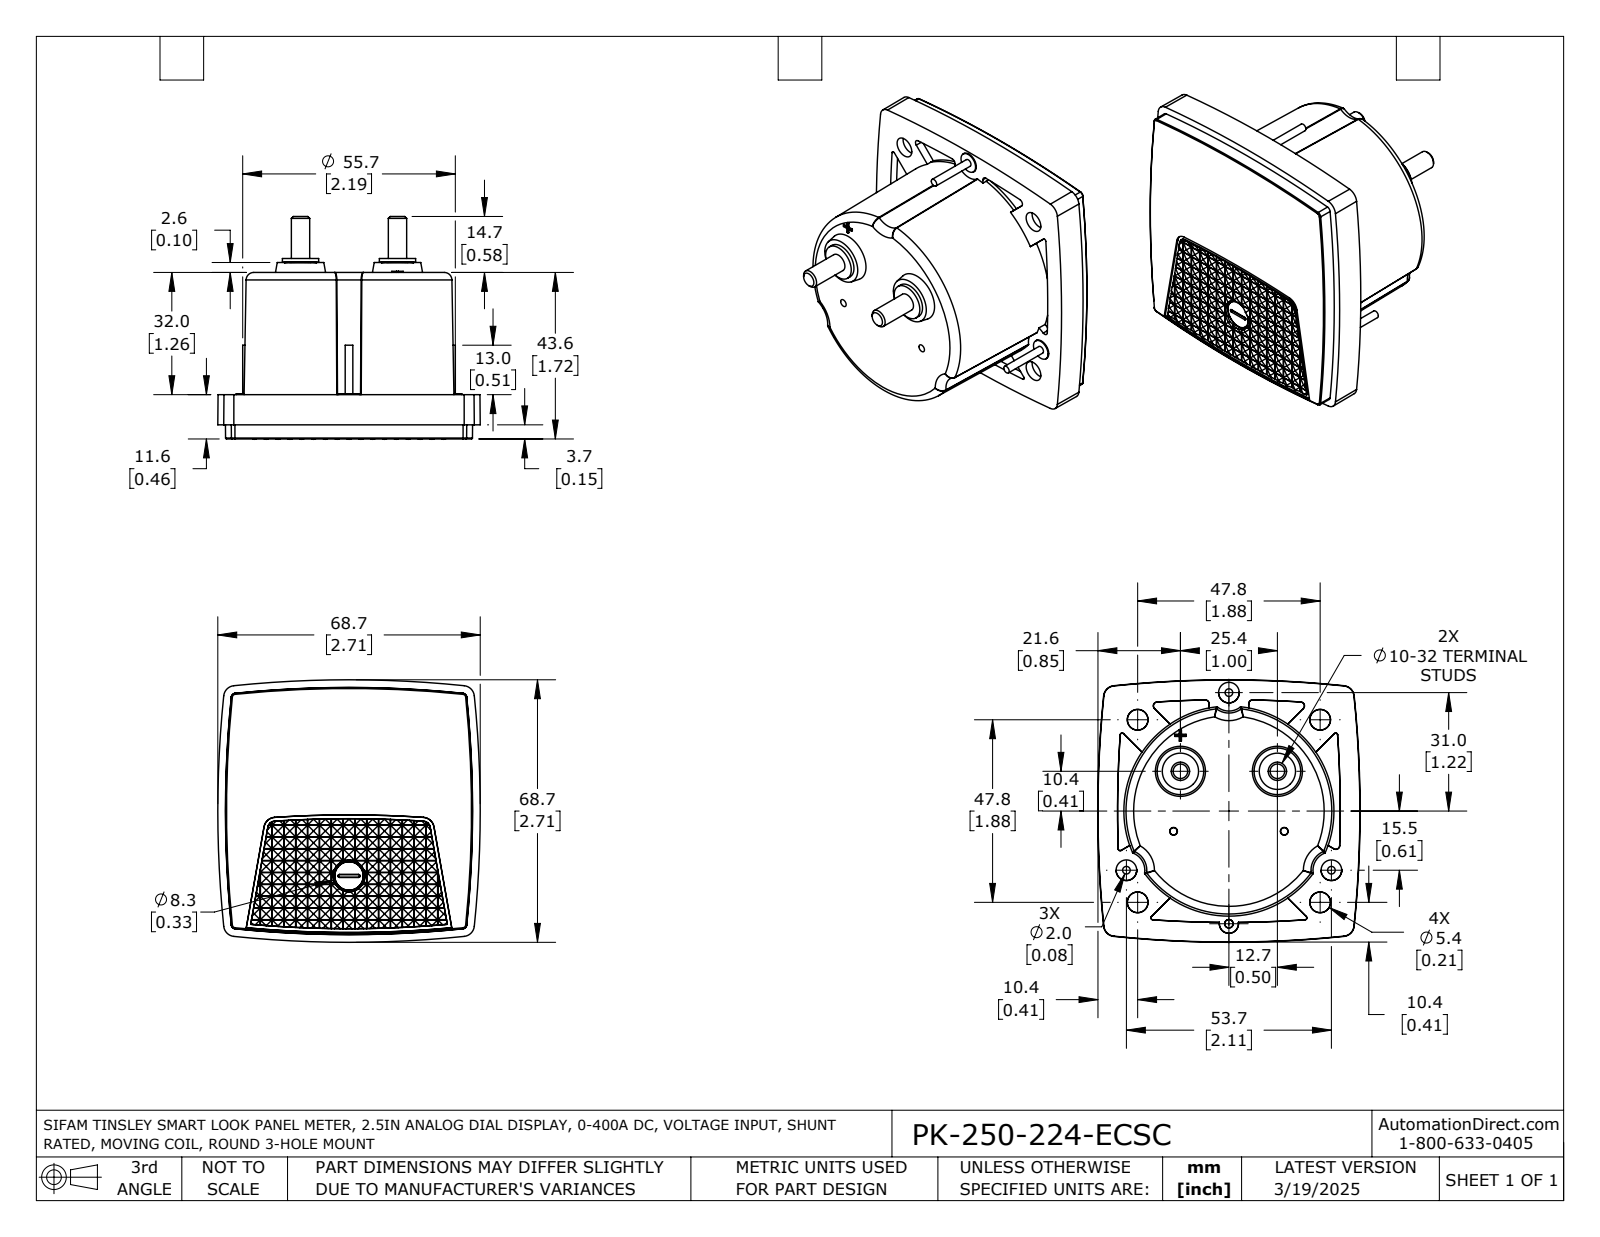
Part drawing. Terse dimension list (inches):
name: PK-250-224-ECSC
written by: SolidWorks 2021 (AUTOMOTIVE_DESIGN)
unit: in
bodies: 1 solid, 1550 faces (1165 planar, 265 cylindrical, 120 other)
size: 2.706 × 2.706 × 2.297
volume: 7.594 in³; area: 30.41 in²
bosses: 3× ⌀0.213, 3× ⌀0.079, 2× ⌀0.374, 2× ⌀0.189, 1× ⌀0.215
rounds: 2× R0.167, 1× R1.083
face distances: 1.717, 1.26, 0.457, 0.024, 0.087, 0.096, 0.311, 0.12, 0.072, 1.346
